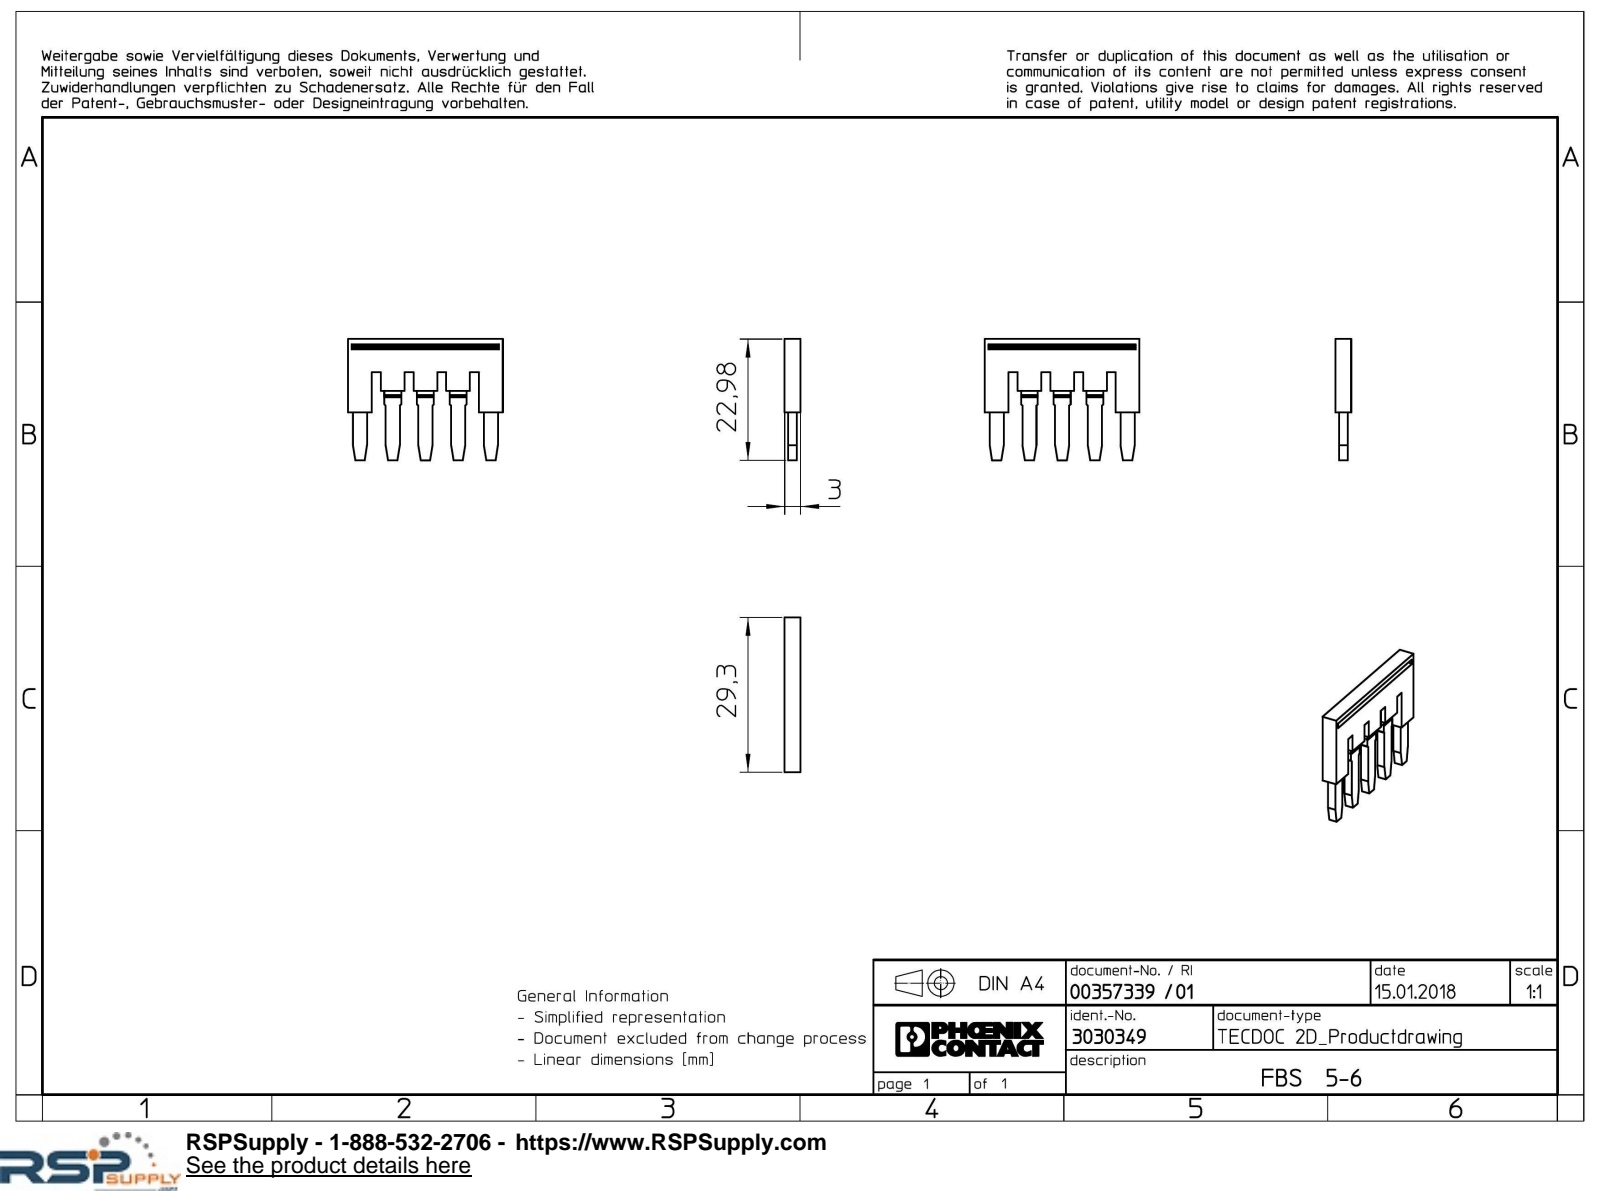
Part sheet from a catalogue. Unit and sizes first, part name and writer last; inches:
Units: inches
Overall size (bounding box): 1.154 × 0.905 × 0.118
Main face-to-face distances: 0.028, 0.091, 0.118, 0.244, 0.063, 0.488, 0.036, 0.141, 0.385, 0.208
Volume: 0.067 in³ · Surface area: 2.384 in²
Bodies: 1 solid, 97 faces (97 planar, 0 cylindrical, 0 other)
Part name (STEP PRODUCT): FBS_5-6_select
STEP written by: Creo Elements/Direct Modeling 20.1A 29-Sep-2018 (C) Parametric Technology GmbH (AUTOMOTIVE_DESIGN)
